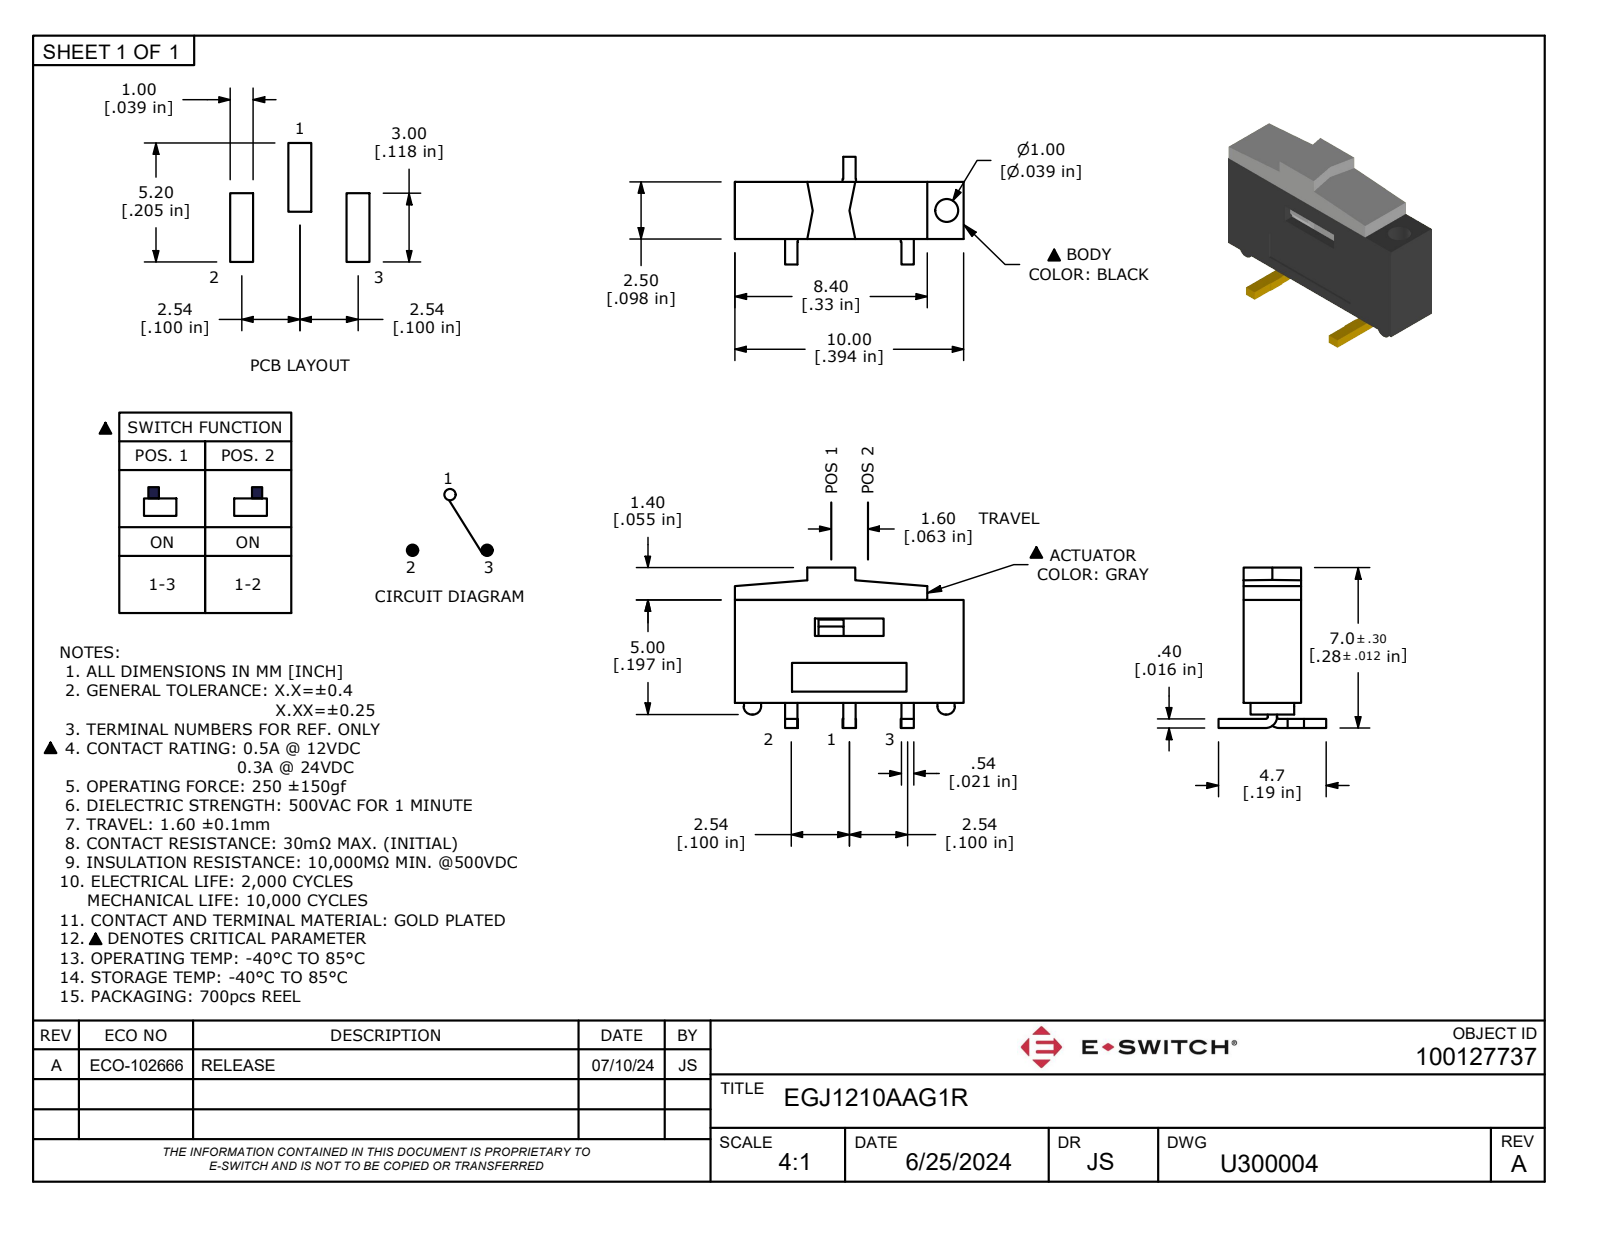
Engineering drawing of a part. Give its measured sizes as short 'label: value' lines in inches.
name: EGJ1210AAG1
written by: Autodesk Inventor 2022 (AUTOMOTIVE_DESIGN)
unit: in
bodies: 1 solid, 111 faces (100 planar, 11 cylindrical, 0 other)
size: 0.394 × 0.276 × 0.185
volume: 0.006 in³; area: 0.508 in²
holes: 1× ⌀0.039
rounds: 4× R0.014, 2× R0.004, 2× R0.02
face distances: 0.017, 0.081, 0.098, 0.02, 0.065, 0.062, 0.079, 0.067, 0.327, 0.394
